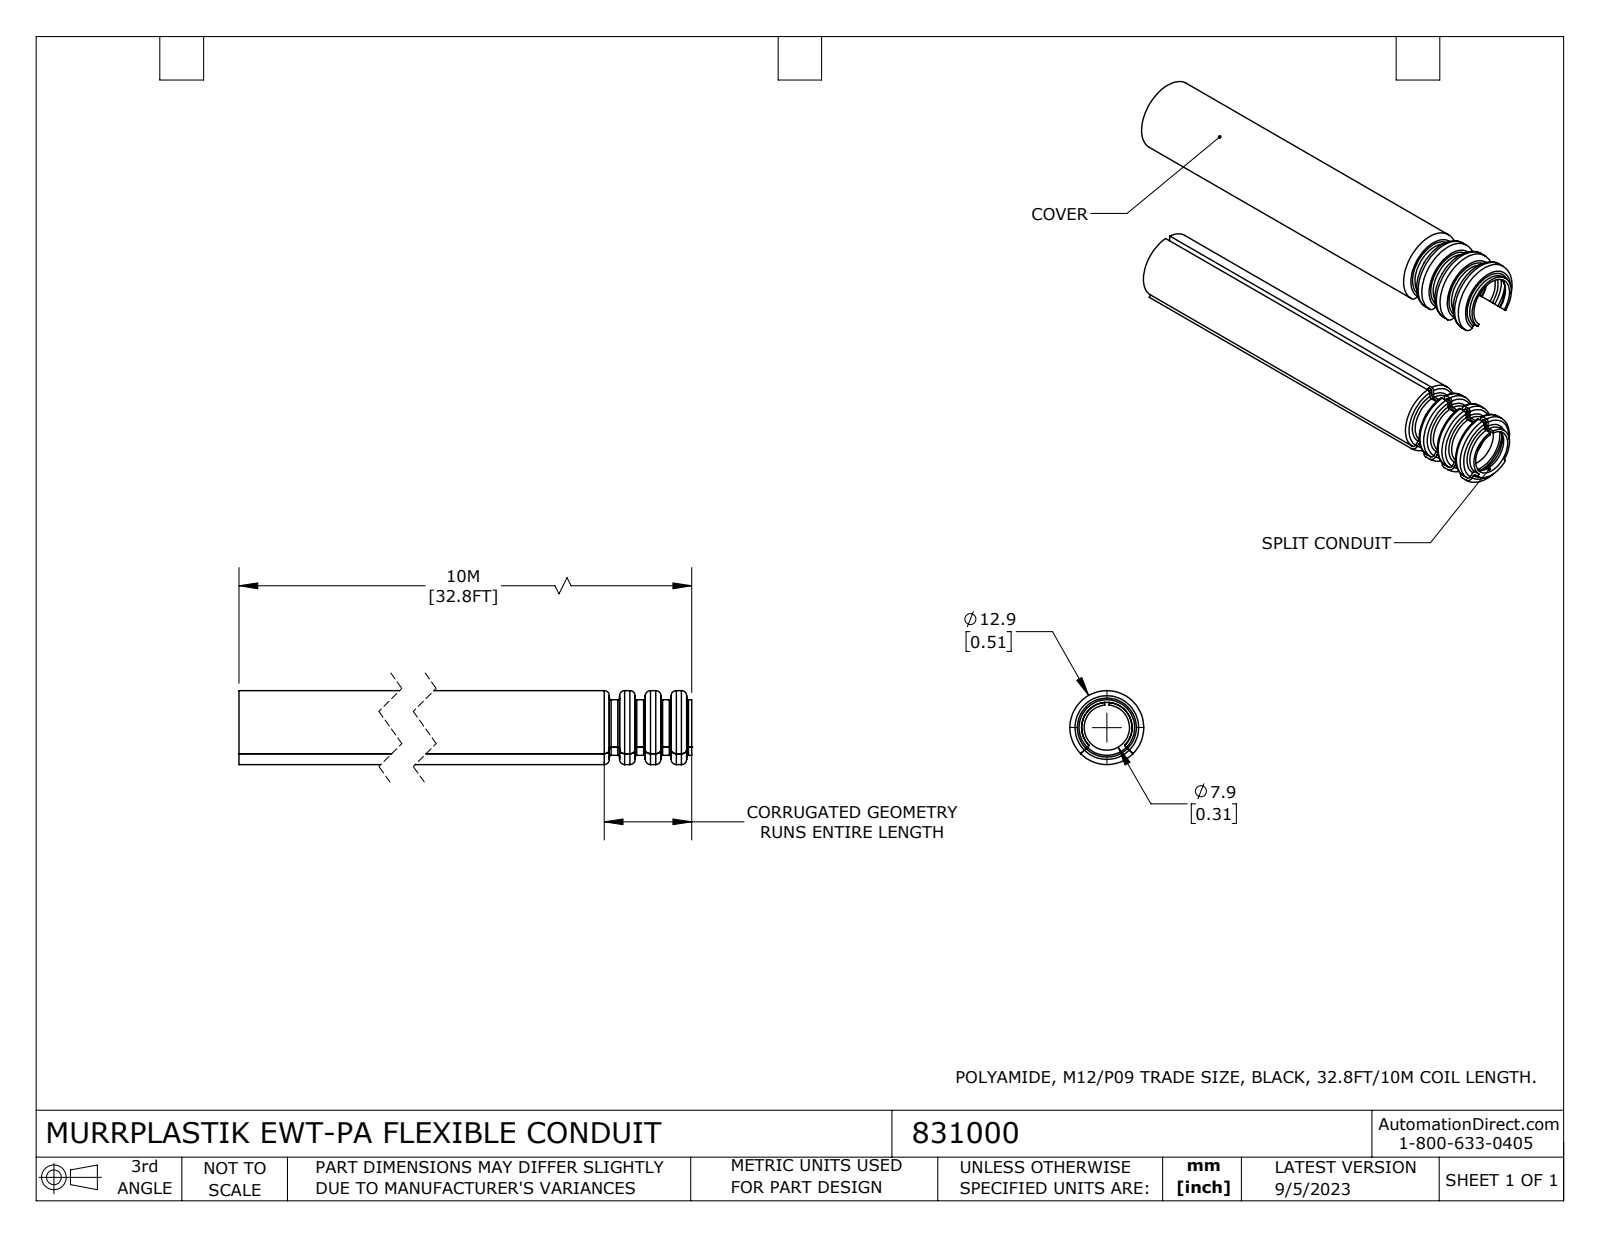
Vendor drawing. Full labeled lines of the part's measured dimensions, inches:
Part name (STEP PRODUCT): 831000
STEP written by: SolidWorks 2021 (CONFIG_CONTROL_DESIGN)
Units: inches
Bodies: 2 solids, 343 faces (10 planar, 107 cylindrical, 226 other)
Overall size (bounding box): 3.15 × 0.508 × 0.508
Volume: 0.355 in³ · Surface area: 16.96 in²
Round holes (diameter × count): ⌀0.311 ×1, ⌀0.437 ×1
Round bosses / shafts (diameter × count): ⌀0.508 ×1, ⌀0.382 ×1
Partial cylindrical surfaces — rounded edges, fillets, slot ends (radius × count): R0.173 ×1, R0.236 ×1
Main face-to-face distances: 3.15
